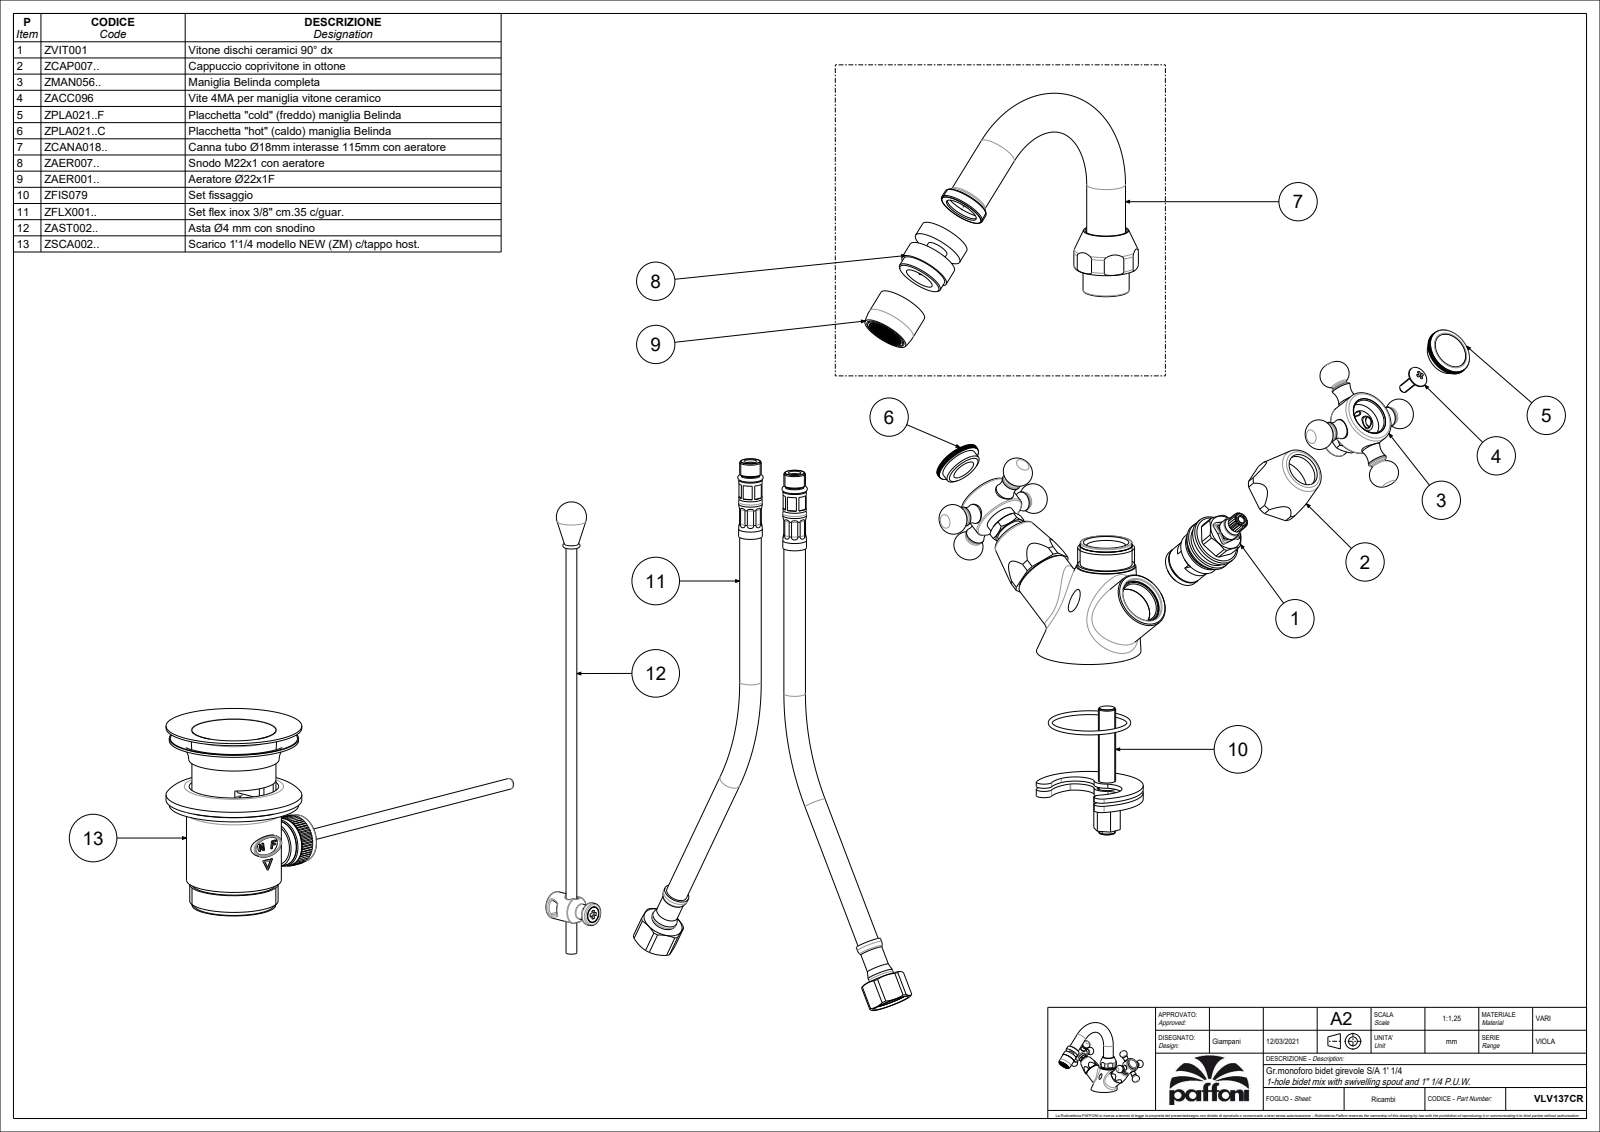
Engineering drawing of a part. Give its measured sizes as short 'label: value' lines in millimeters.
name: VLV137CR
written by: CREO PARAMETRIC BY PTC INC, 2020044 (CONFIG_CONTROL_DESIGN)
unit: mm
bodies: 2 solids, 954 faces (464 planar, 306 cylindrical, 184 other)
size: 175.57 × 147.23 × 132.5
volume: 188 893 mm³; area: 39 433 mm²
holes: 1× ⌀5.5
bosses: 6× ⌀9, 6× ⌀7, 2× ⌀26.3, 2× ⌀25, 2× ⌀18, 2× ⌀14, 2× ⌀13, 1× ⌀26.4
rounds: 2× R11, 2× R14.5, 1× R15
face distances: 26.49, 5, 28.5, 23.7, 28.7, 11.2, 20.75, 35.21, 24.01, 26.5
